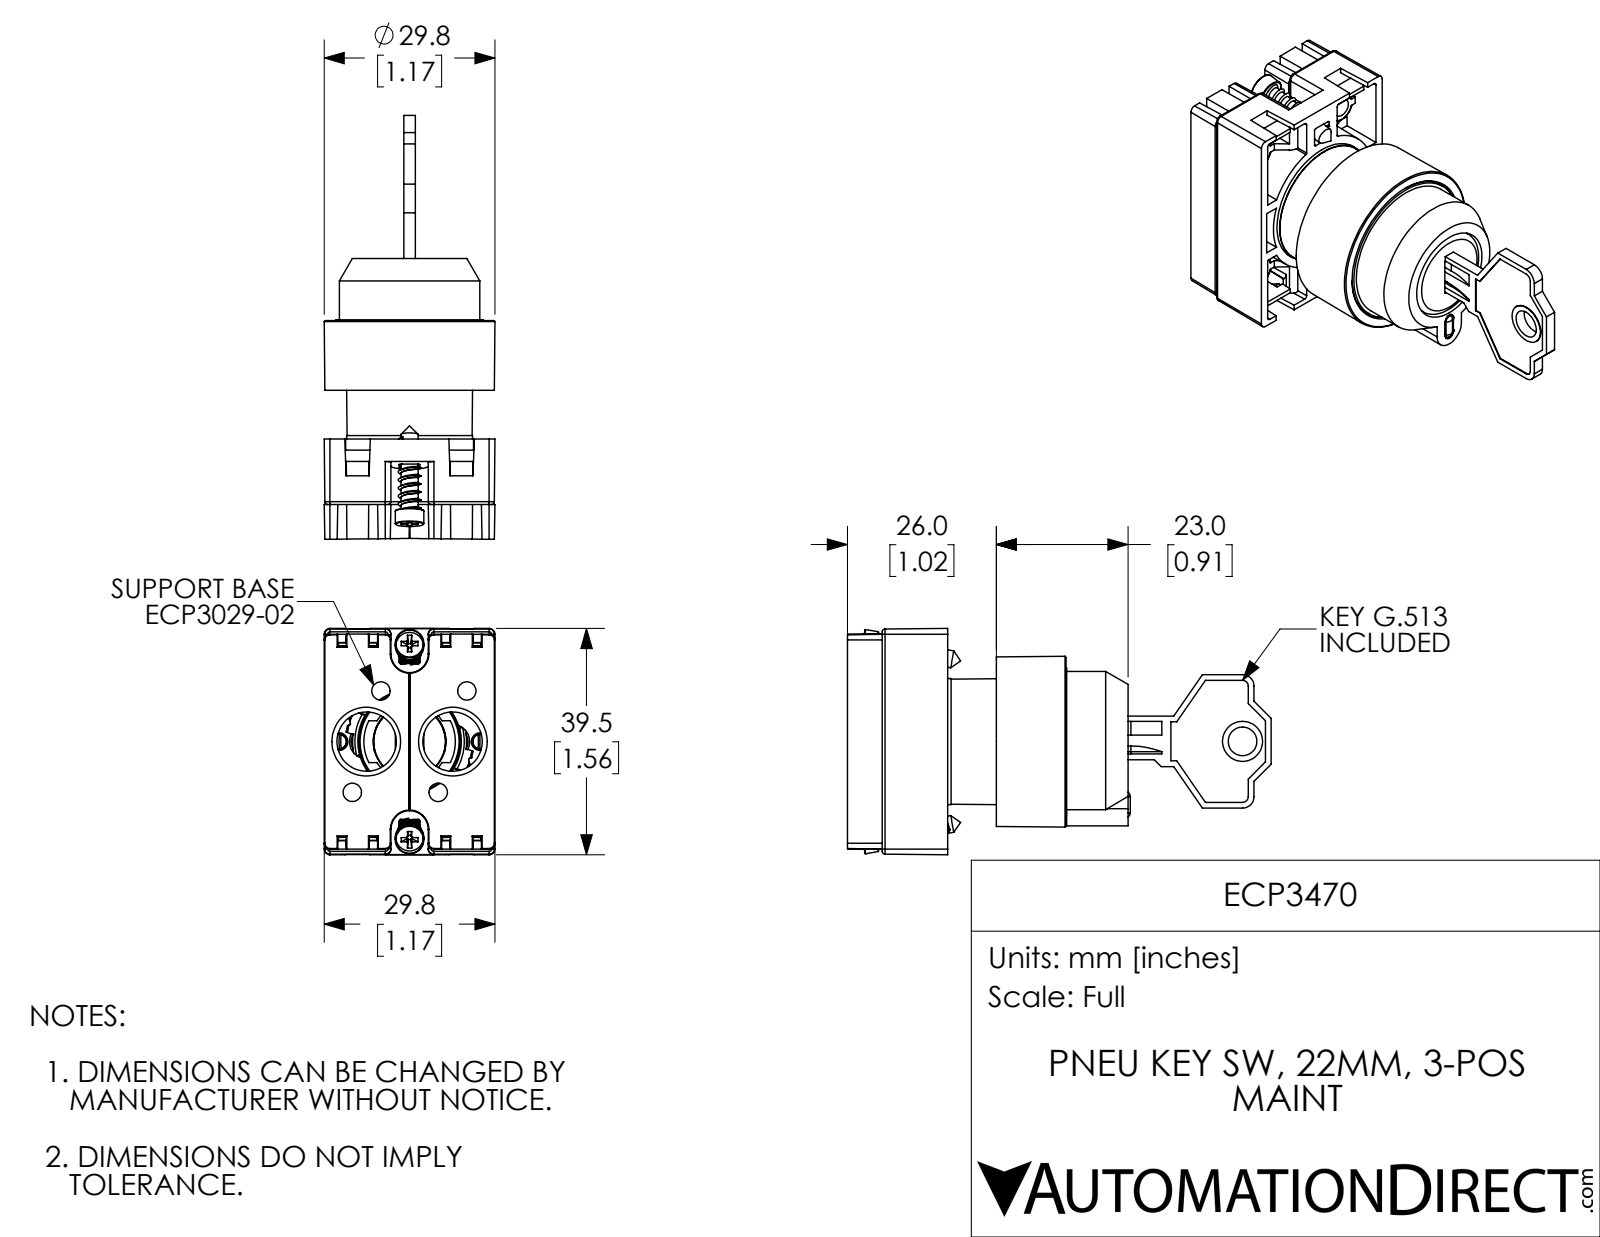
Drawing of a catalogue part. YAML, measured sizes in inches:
part_name: "ECP3470"
step_written_by: "SolidWorks 2017 (AUTOMOTIVE_DESIGN)"
units: inches
bodies: {solids: 10, faces: 961, planar: 491, cylindrical: 184, other: 286}
overall_size: [2.913, 1.555, 1.173]
volume: 1.241
surface_area: 36.38
round_holes:
  - {diameter: 0.081, count: 4}
  - {diameter: 0.407, count: 2}
  - {diameter: 0.094, count: 1}
  - {diameter: 0.197, count: 1}
  - {diameter: 0.5, count: 1}
  - {diameter: 0.634, count: 1}
  - {diameter: 0.697, count: 1}
  - {diameter: 0.75, count: 1}
  - {diameter: 0.752, count: 1}
  - {diameter: 0.854, count: 1}
  - {diameter: 0.976, count: 1}
  - {diameter: 1.024, count: 1}
round_bosses_or_shafts:
  - {diameter: 0.197, count: 2}
  - {diameter: 0.118, count: 2}
  - {diameter: 1.012, count: 1}
  - {diameter: 0.965, count: 1}
  - {diameter: 0.866, count: 1}
  - {diameter: 0.85, count: 1}
  - {diameter: 0.618, count: 1}
  - {diameter: 0.492, count: 1}
partial_cylinders:
  - {radius: 0.02, count: 18}
  - {radius: 0.039, count: 12}
  - {radius: 0.012, count: 10}
  - {radius: 0.006, count: 8}
  - {radius: 0.008, count: 4}
  - {radius: 0.118, count: 3}
  - {radius: 0.008, count: 2}
  - {radius: 0.079, count: 2}
face_to_face_distances: [0.079, 0.067, 0.075, 0.083, 0.715, 0.827, 0.451, 0.587, 0.966, 0.102]
hole_center_spacings: [0.304, 0.541, 0.817, 0.295, 0.472, 0.972, 1.081, 0.591]
